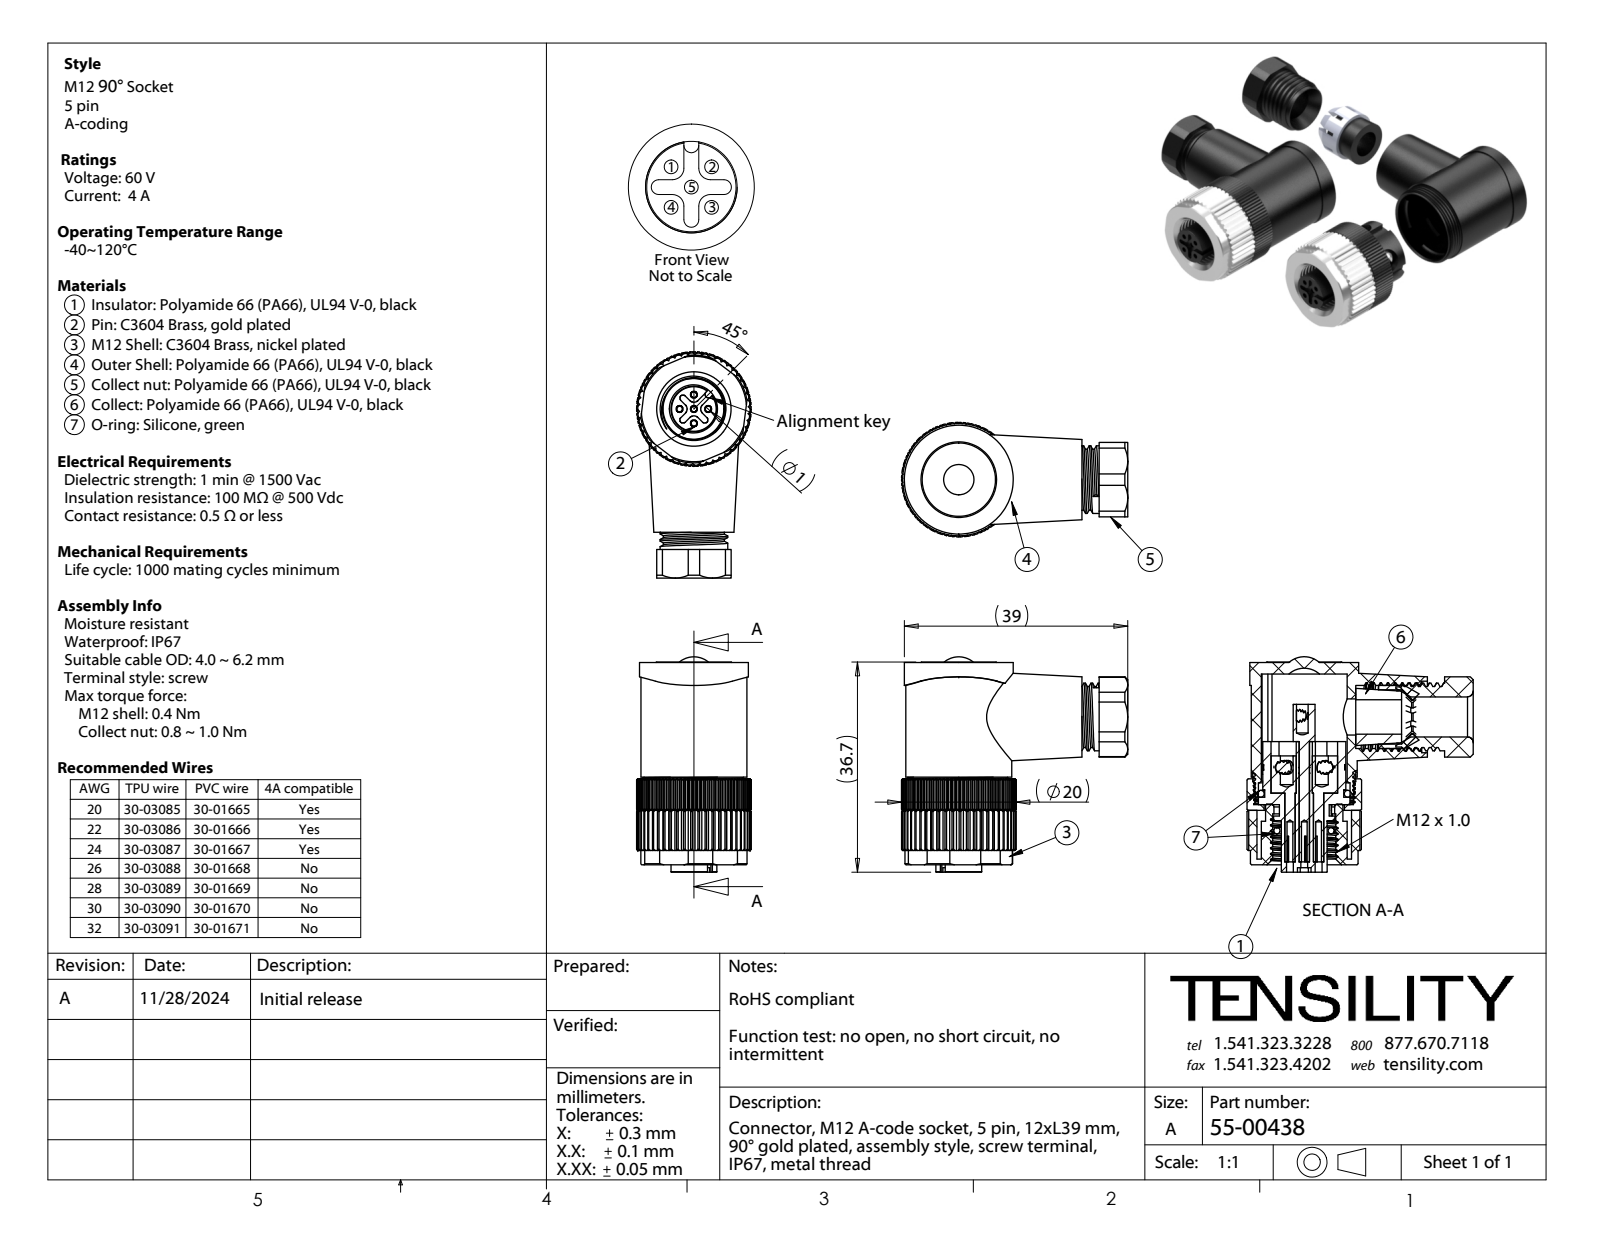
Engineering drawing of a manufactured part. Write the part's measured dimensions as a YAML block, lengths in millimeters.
part_name: "55-00438-08; 55-00438_revA; 55-00438-11; 55-00438-01 (+8 more)"
step_written_by: "SolidWorks 2021 (CONFIG_CONTROL_DESIGN)"
units: millimeters
bodies: {solids: 18, faces: 1520, planar: 543, cylindrical: 518, other: 459}
overall_size: [39.5, 37.6, 20]
volume: 8882
surface_area: 14261
round_holes:
  - {diameter: 2.5, count: 9}
  - {diameter: 1, count: 5}
  - {diameter: 1.2, count: 5}
  - {diameter: 2.05, count: 5}
  - {diameter: 1.8, count: 4}
  - {diameter: 5, count: 4}
  - {diameter: 11, count: 2}
  - {diameter: 6, count: 1}
  - {diameter: 6.3, count: 1}
  - {diameter: 7, count: 1}
  - {diameter: 9.5, count: 1}
  - {diameter: 10.6, count: 1}
round_bosses_or_shafts:
  - {diameter: 3.5, count: 5}
  - {diameter: 2.4, count: 5}
  - {diameter: 19, count: 1}
  - {diameter: 18.5, count: 1}
  - {diameter: 17.8, count: 1}
  - {diameter: 17.03, count: 1}
  - {diameter: 17, count: 1}
  - {diameter: 14.5, count: 1}
partial_cylinders:
  - {radius: 1.75, count: 5}
  - {radius: 1, count: 4}
  - {radius: 0.55, count: 3}
  - {radius: 0.6, count: 1}
  - {radius: 6.45, count: 1}
  - {radius: 6.5, count: 1}
  - {radius: 7, count: 1}
  - {radius: 9.4, count: 1}
face_to_face_distances: [1, 2, 22.8, 24.8, 25.8, 9.5, 11.8, 12.5, 13.44, 13.8]
hole_center_spacings: [5.14, 5.13, 0.8, 2.5, 3.12, 3.54, 3.62, 4.34]
